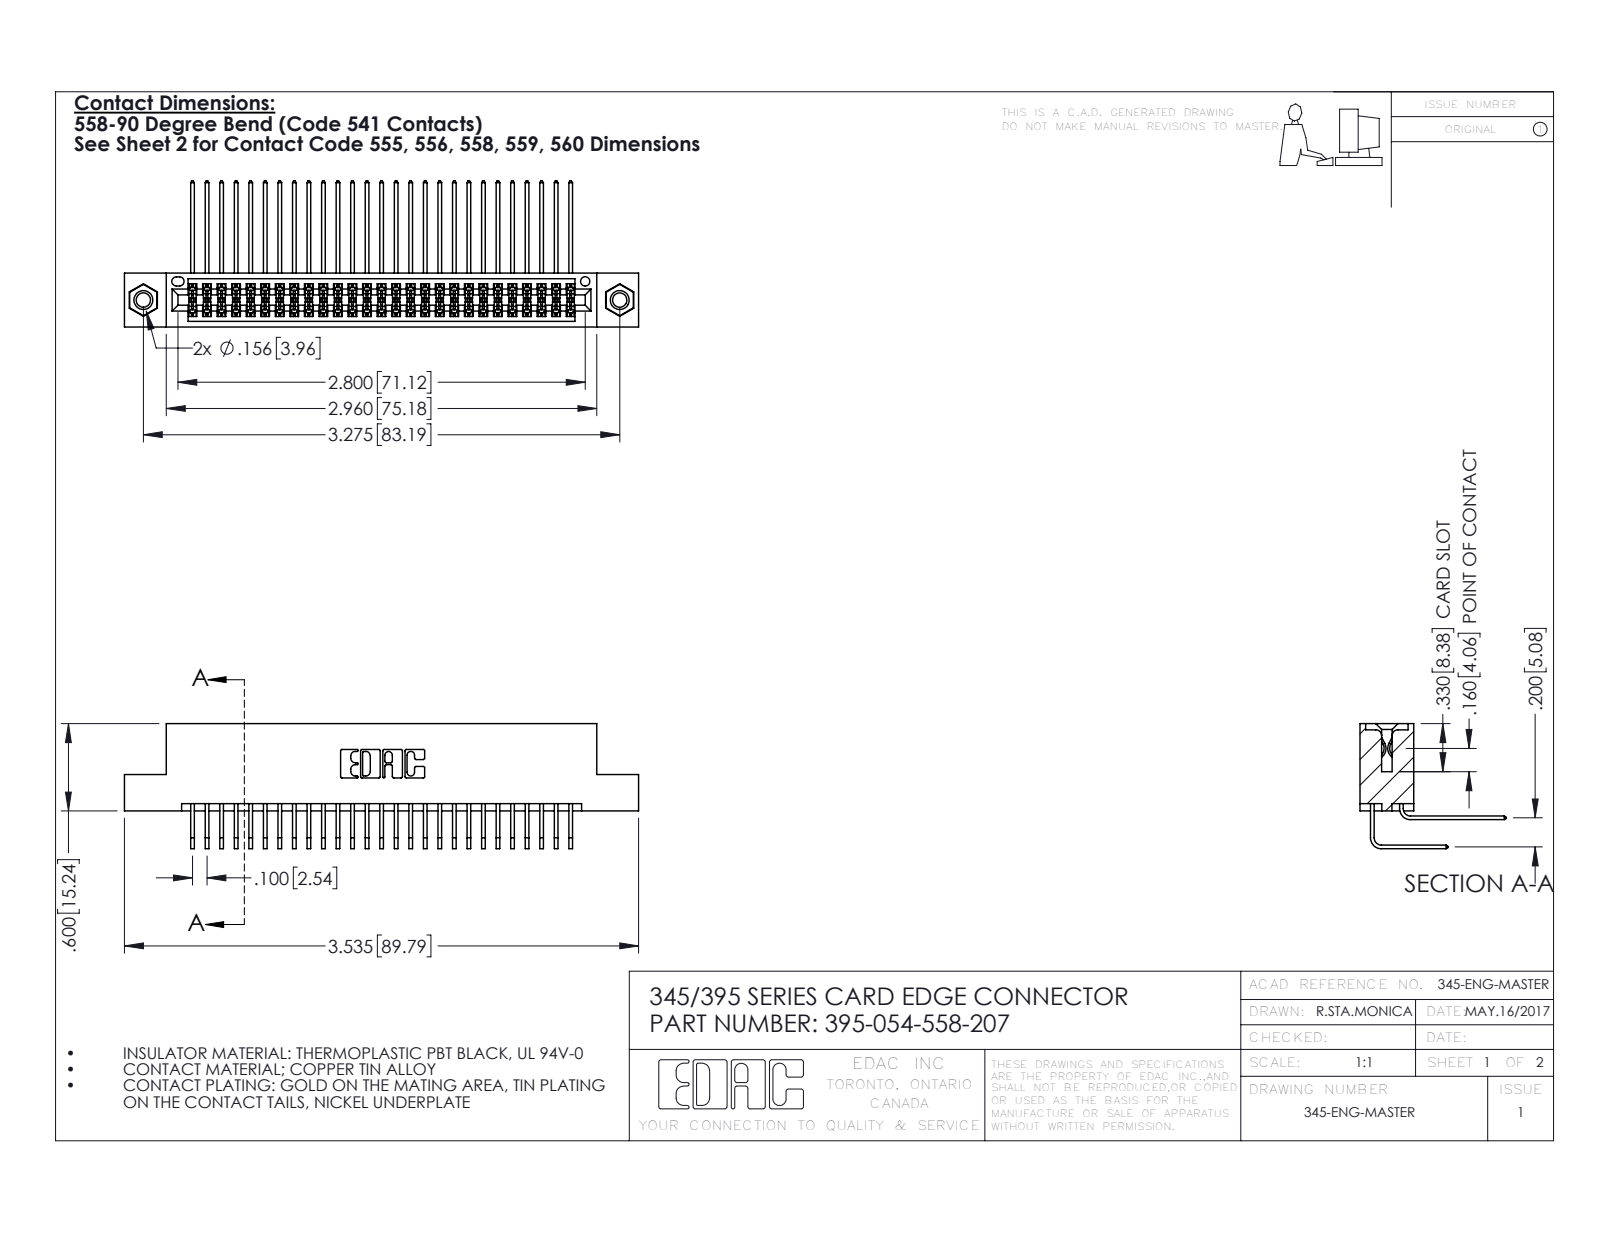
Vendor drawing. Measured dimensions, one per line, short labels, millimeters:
name: 345-250-001_345-250-005-103; 345-292-001_558 559 Tail - 1; 345-292-001_558 Tail - 2; 395-054-558-207 (+1 more)
written by: SolidWorks 2016 (CONFIG_CONTROL_DESIGN)
unit: mm
bodies: 57 solids, 2994 faces (2002 planar, 976 cylindrical, 16 other)
size: 89.8 × 25.5 × 21.8
volume: 8 880 mm³; area: 14 330 mm²
holes: 2× ⌀2.5, 2× ⌀3.2, 2× ⌀4, 1× ⌀1.6
bosses: 2× ⌀3.9
rounds: 82× R0.2, 22× R0.3, 6× R0.2, 6× R0.8, 3× R0.7, 2× R0.4, 2× R0.5, 2× R0.6
face distances: 5.1, 1.8, 7.6, 9.4, 2.5, 6.9, 0.6, 5.7, 0.6, 7.2
hole spacings: 6.9, 77.2, 83.2
